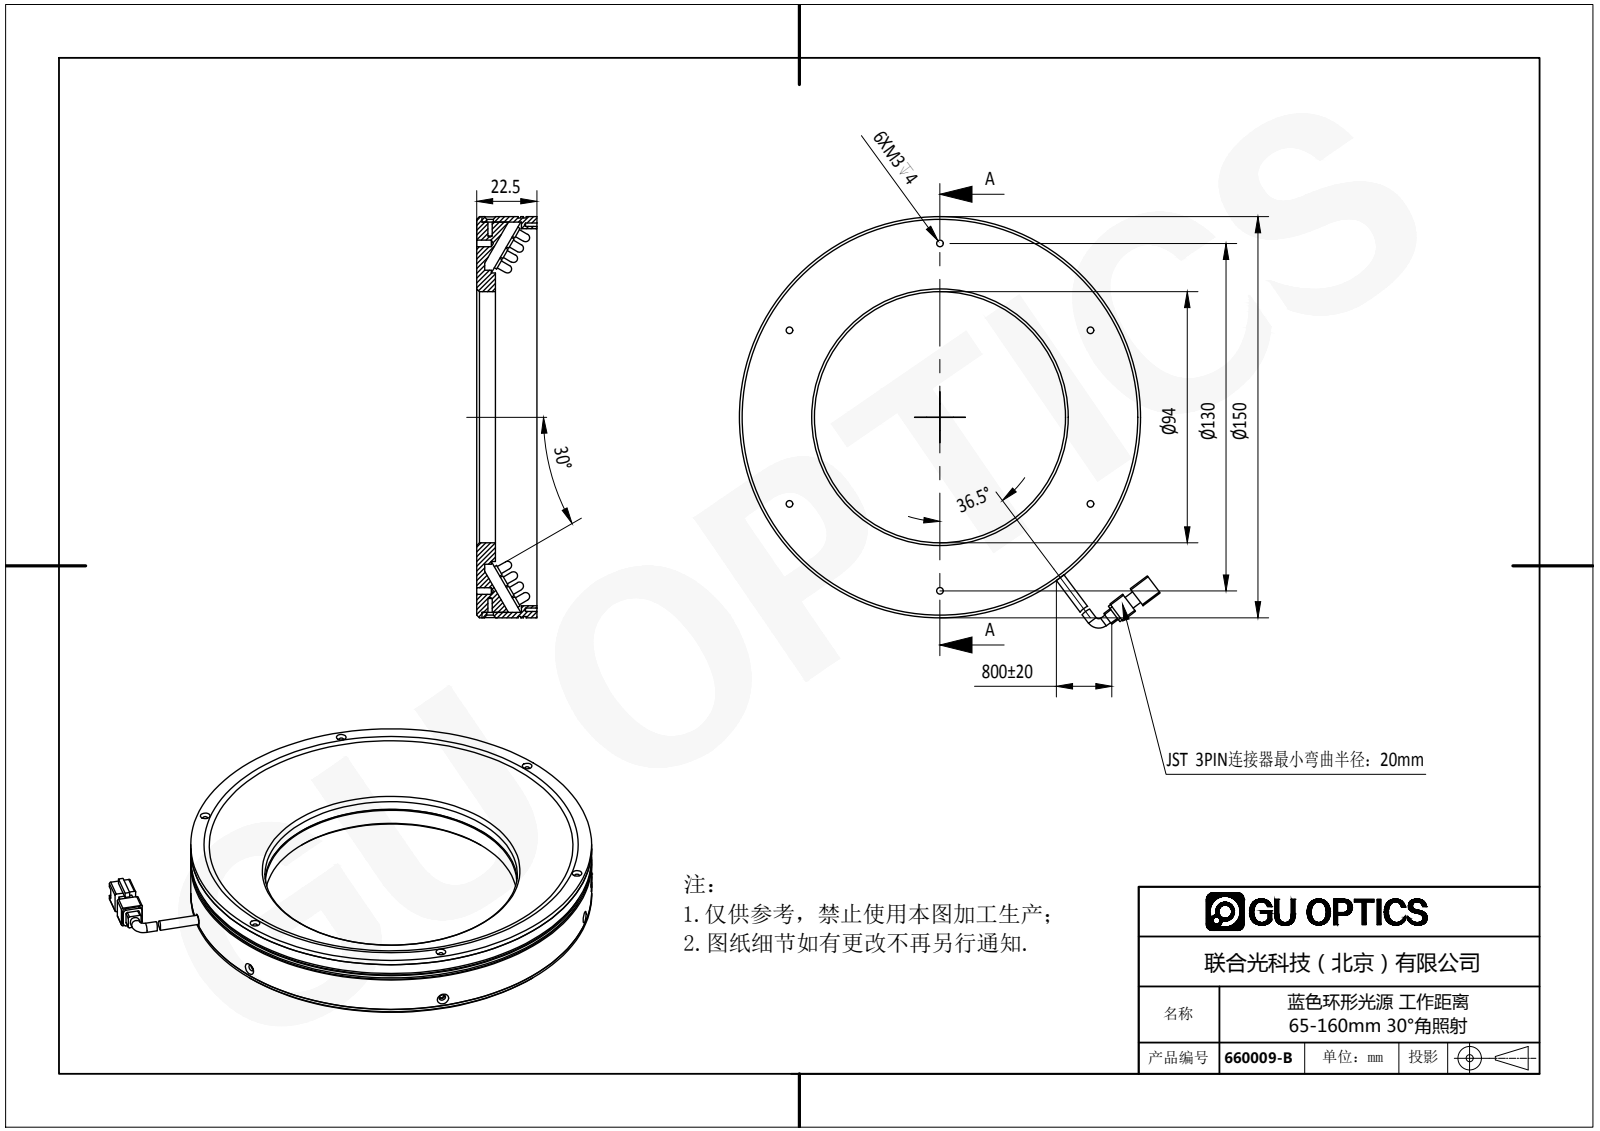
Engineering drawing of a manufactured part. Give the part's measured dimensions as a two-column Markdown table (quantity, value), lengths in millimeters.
| quantity | value |
| --- | --- |
| part name | 660009-B |
| STEP written by | SolidWorks 2016 (AUTOMOTIVE_DESIGN) |
| units | millimeters |
| bodies | 341 solids, 6006 faces (4098 planar, 1478 cylindrical, 430 other) |
| overall size | 160.52 × 150 × 24.75 |
| volume | 136 685 mm³ |
| surface area | 129 773 mm² |
| round holes (diameter × count) | 1.25 × 6, 1.7 × 6, 2.5 × 6, 1.6 × 5, 2.4 × 5, 3.5 × 4, 94 × 1, 94.4 × 1, 141 × 1 |
| round bosses / shafts (diameter × count) | 3.8 × 335, 3 × 335, 3.5 × 2, 150 × 1, 149 × 1, 146 × 1, 110 × 1, 108 × 1 |
| partial cylindrical surfaces (radius × count) | 0.5 × 8, 1 × 4, 1.65 × 1, 10 × 1 |
| main face-to-face distances | 22.5, 2, 15.5, 7, 1, 17.5, 5, 24.5, 20.5, 3 |
| hole center spacings | 65, 68.77, 118.7, 72, 112.58, 124.71, 137, 7 |
